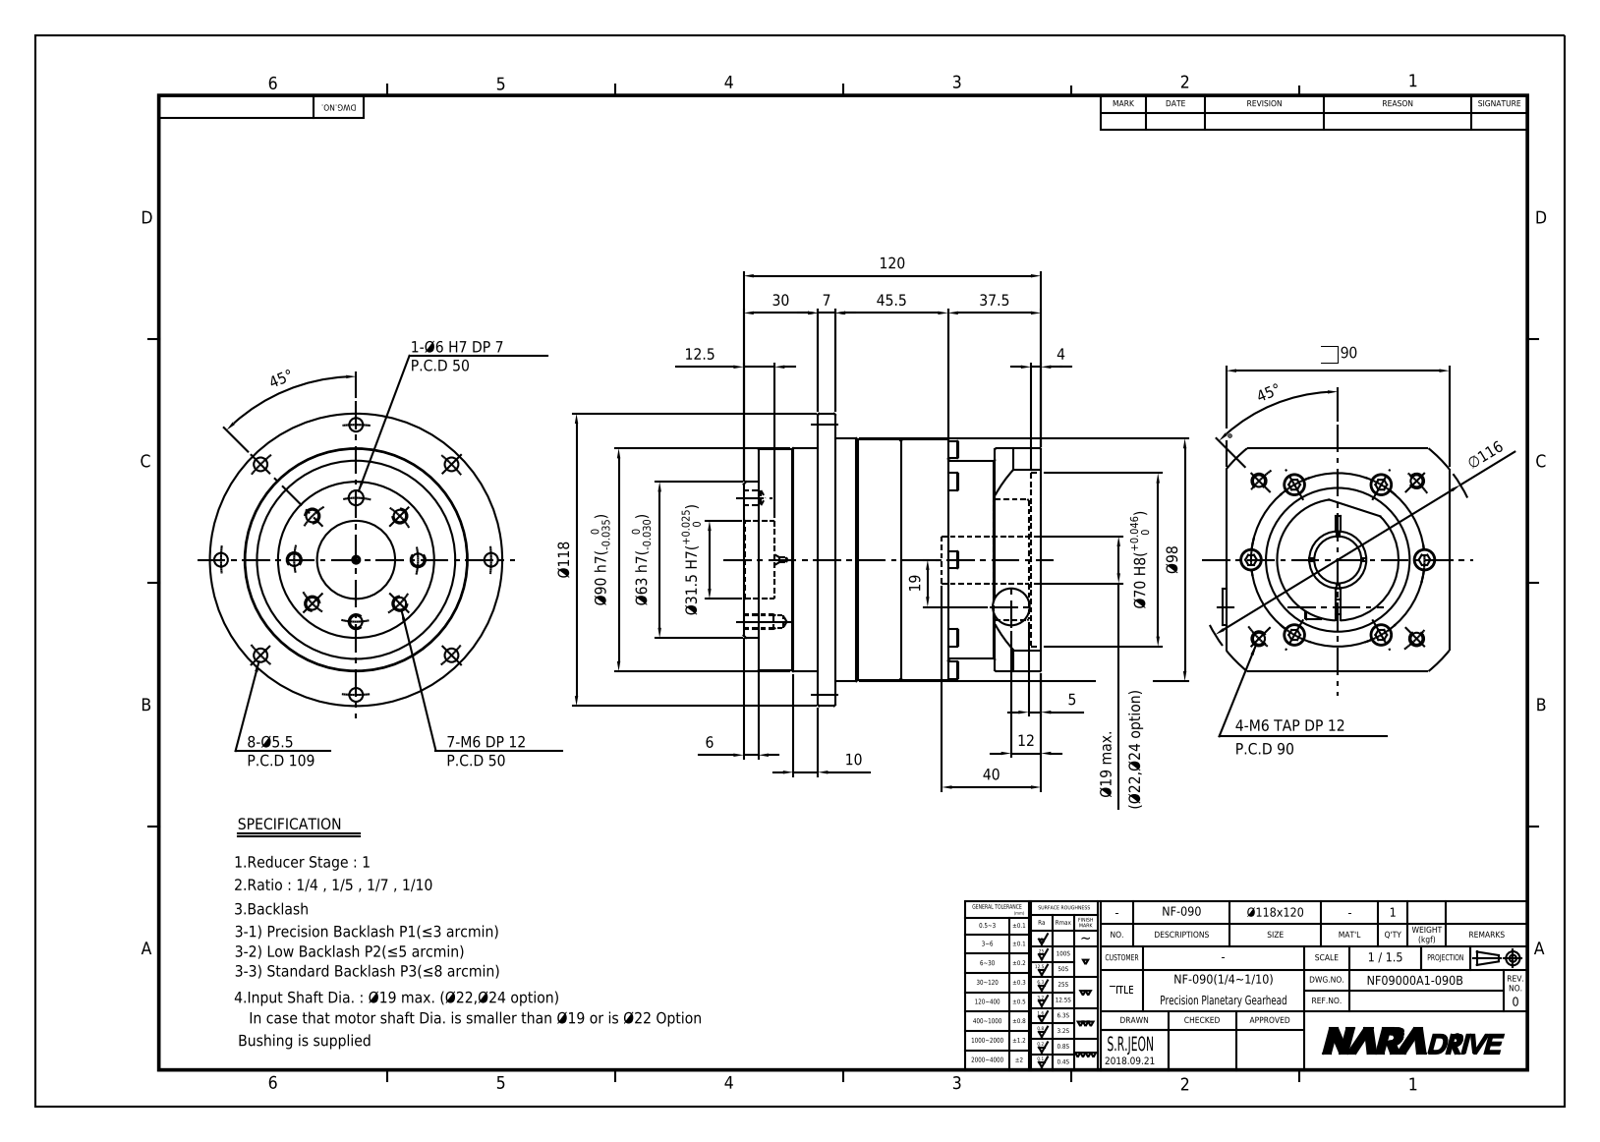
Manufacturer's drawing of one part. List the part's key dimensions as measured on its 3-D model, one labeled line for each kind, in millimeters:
Part name (STEP PRODUCT): NF09000B1-090B
STEP written by: Autodesk Inventor 2015 (AUTOMOTIVE_DESIGN)
Units: millimetres
Bodies: 2 solids, 471 faces (209 planar, 133 cylindrical, 129 other)
Overall size (bounding box): 119.5 × 118 × 118
Volume: 571 433 mm³ · Surface area: 118 214 mm²
Round holes (diameter × count): ⌀5.5 ×14, ⌀4.92 ×12, ⌀3.24 ×8, ⌀4.5 ×8, ⌀4.13 ×6, ⌀9 ×6, ⌀2 ×1, ⌀6 ×1, ⌀6.6 ×1, ⌀7 ×1, ⌀8.5 ×1, ⌀19 ×1
Round bosses / shafts (diameter × count): ⌀7 ×8, ⌀4 ×8, ⌀8.5 ×6, ⌀5 ×6, ⌀118 ×1, ⌀98 ×1, ⌀97 ×1, ⌀90 ×1
Partial cylindrical surfaces — rounded edges, fillets, slot ends (radius × count): R0.5 ×8, R5.5 ×1, R35 ×1, R58 ×1
Main face-to-face distances: 82.5, 7, 64, 37, 19, 18.5, 33.5, 89.5, 56, 45.5
Hole centre spacings: 35, 25, 54.5, 77.08, 92, 9.5, 39.09, 41.71
